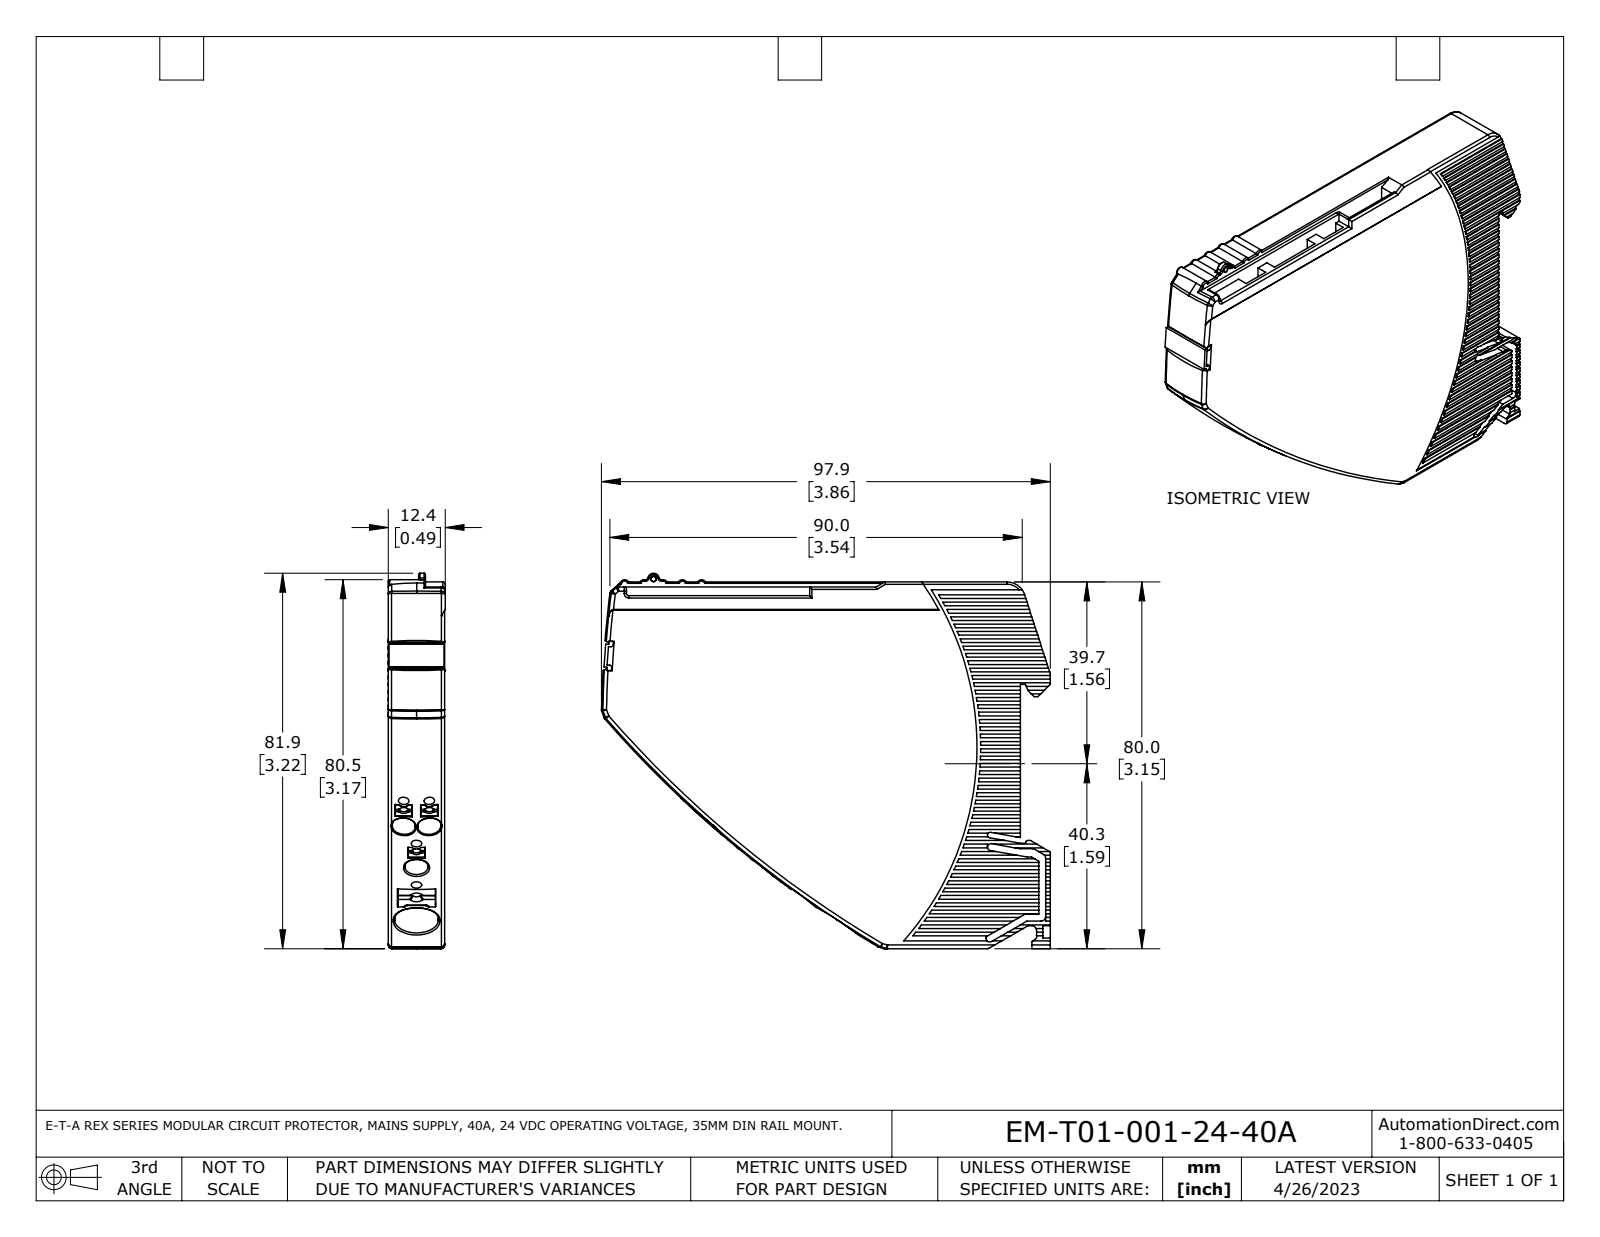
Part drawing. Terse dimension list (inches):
name: t-em12-t01-xxx_ik01_REV1
written by: SolidWorks 2021 (AUTOMOTIVE_DESIGN)
unit: in
bodies: 1 solid, 1092 faces (727 planar, 241 cylindrical, 124 other)
size: 3.856 × 3.224 × 0.488
volume: 4.325 in³; area: 31.37 in²
holes: 4× ⌀0.091, 1× ⌀0.044
rounds: 27× R0.039, 12× R0.012, 12× R0.02, 10× R0.012, 10× R0.031, 9× R0.008, 6× R0.03, 6× R0.098
face distances: 0.484, 0.476, 0.469, 0.098, 0.059, 0.039, 0.033, 0.126, 0.134, 0.067
hole spacings: 0.562, 1.131, 0.22, 0.575
